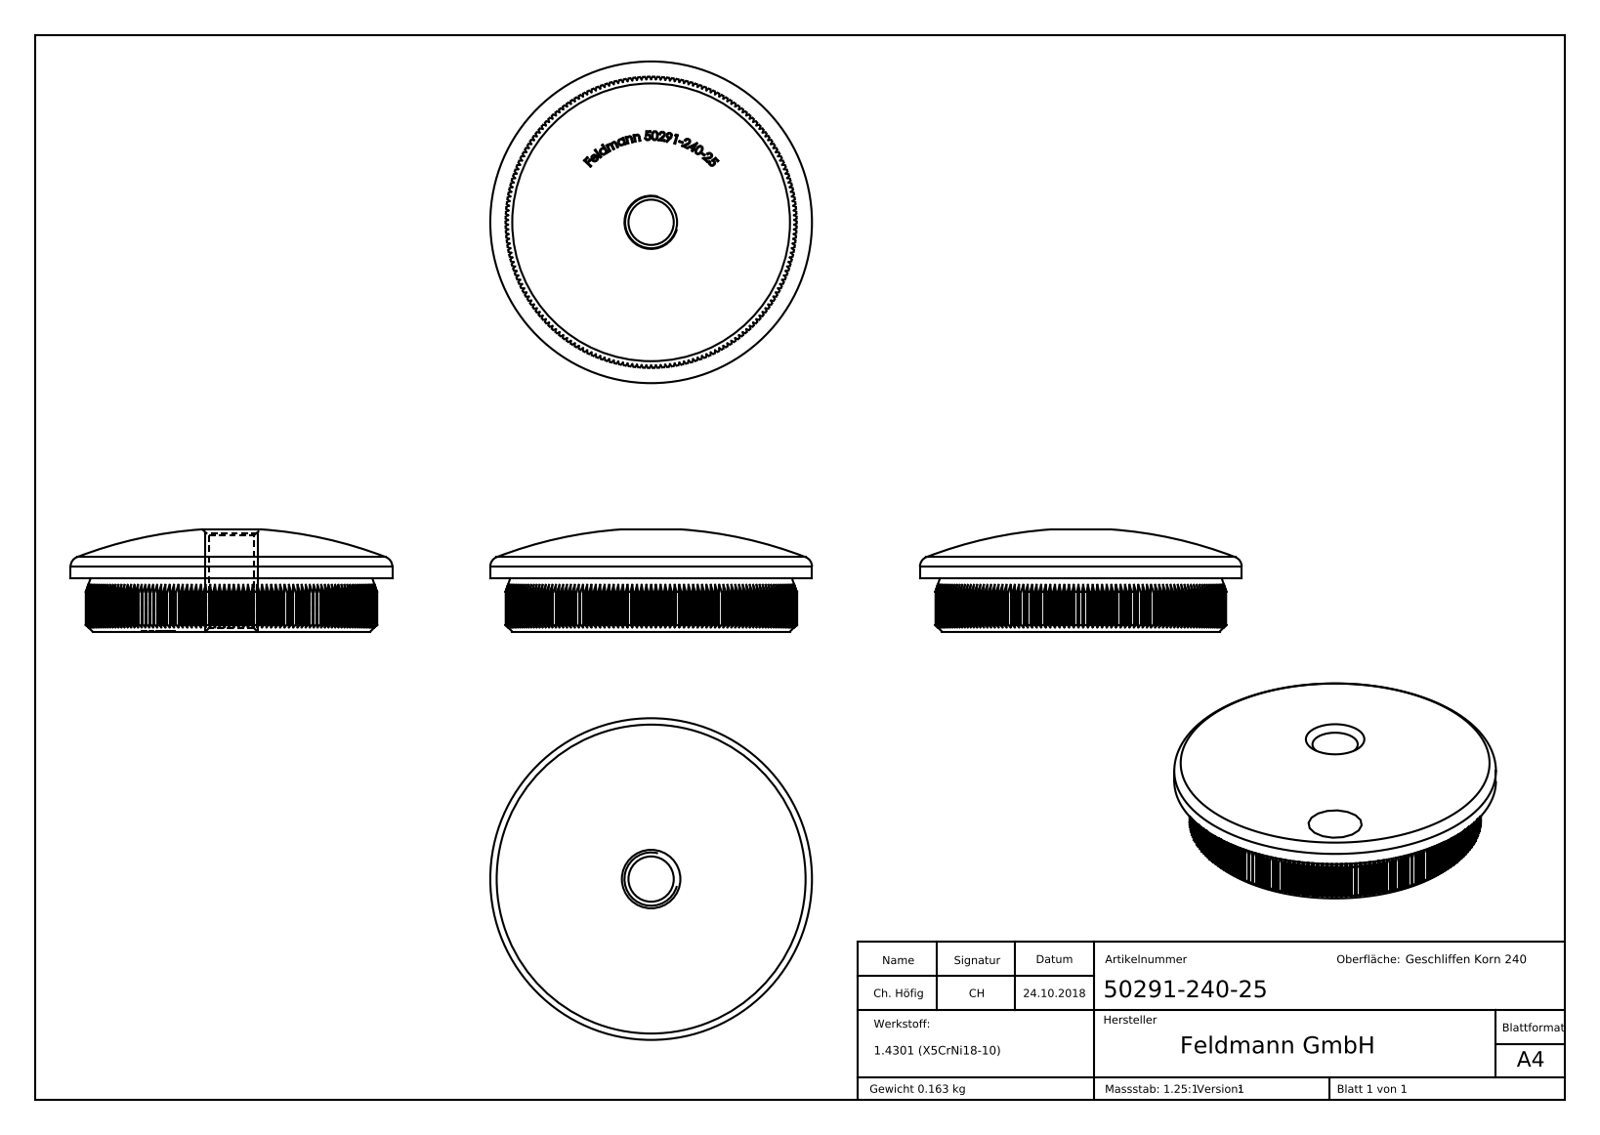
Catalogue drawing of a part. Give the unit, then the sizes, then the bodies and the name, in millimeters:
Units: millimetres
Overall size (bounding box): 48.3 × 48.3 × 15.35
Round holes (diameter × count): ⌀6.8 ×1
Round bosses / shafts (diameter × count): ⌀48.3 ×1
Partial cylindrical surfaces — rounded edges, fillets, slot ends (radius × count): R21.85 ×1
Main face-to-face distances: 8, 21.5, 21.48, 21.52, 7.9, 0.66, 0.54, 0.67, 0.79, 0.72
Volume: 20 650 mm³ · Surface area: 5 918 mm²
Bodies: 1 solid, 813 faces (512 planar, 194 cylindrical, 107 other)
Part name (STEP PRODUCT): 50291-240-25
STEP written by: SolidWorks 2015 (CONFIG_CONTROL_DESIGN)
